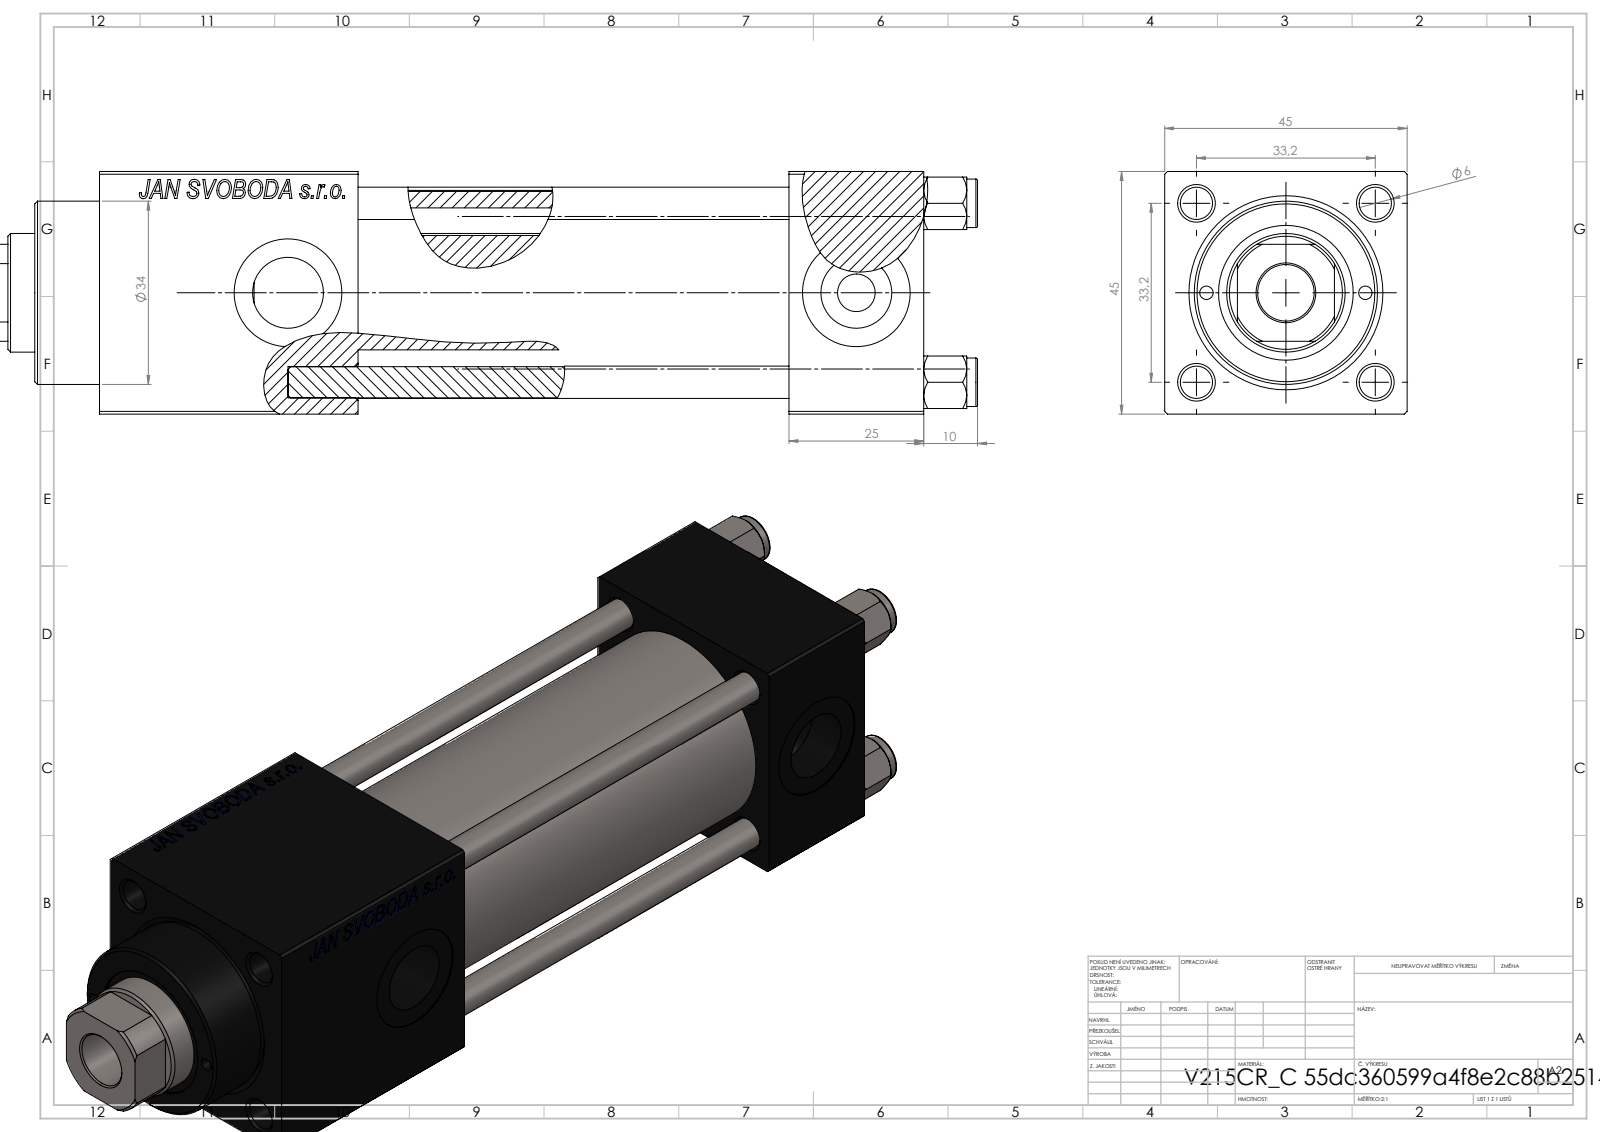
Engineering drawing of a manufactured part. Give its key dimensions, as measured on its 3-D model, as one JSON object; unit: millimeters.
{"part_name": "V215CR_C_TYCINKA; NUT_M5_C; V215CR_VCP_C; V215_VC_A (+1 more)", "step_written_by": "SolidWorks 2019 (CONFIG_CONTROL_DESIGN)", "units": "millimeters", "bodies": {"solids": 11, "faces": 1153, "planar": 527, "cylindrical": 90, "other": 536}, "overall_size": [188, 45, 45], "volume_mm3": 234636, "surface_area_mm2": 82437, "round_holes": [[6, 4], [2.5, 2], [7, 2], [13.16, 2], [20, 2], [10.5, 1], [22, 1], [24, 1], [25, 1], [32, 1], [33, 1]], "round_bosses_or_shafts": [[9, 4], [38, 1], [34, 1]], "partial_cylinders_radius": [[10.5, 1]], "face_to_face_distances": [45, 25, 153, 105, 80, 128, 48, 124.3, 99.3, 19.3], "hole_center_spacings": [16.7, 23.48, 33.2, 35.47, 14.75, 46.95, 29.5, 105.5]}
